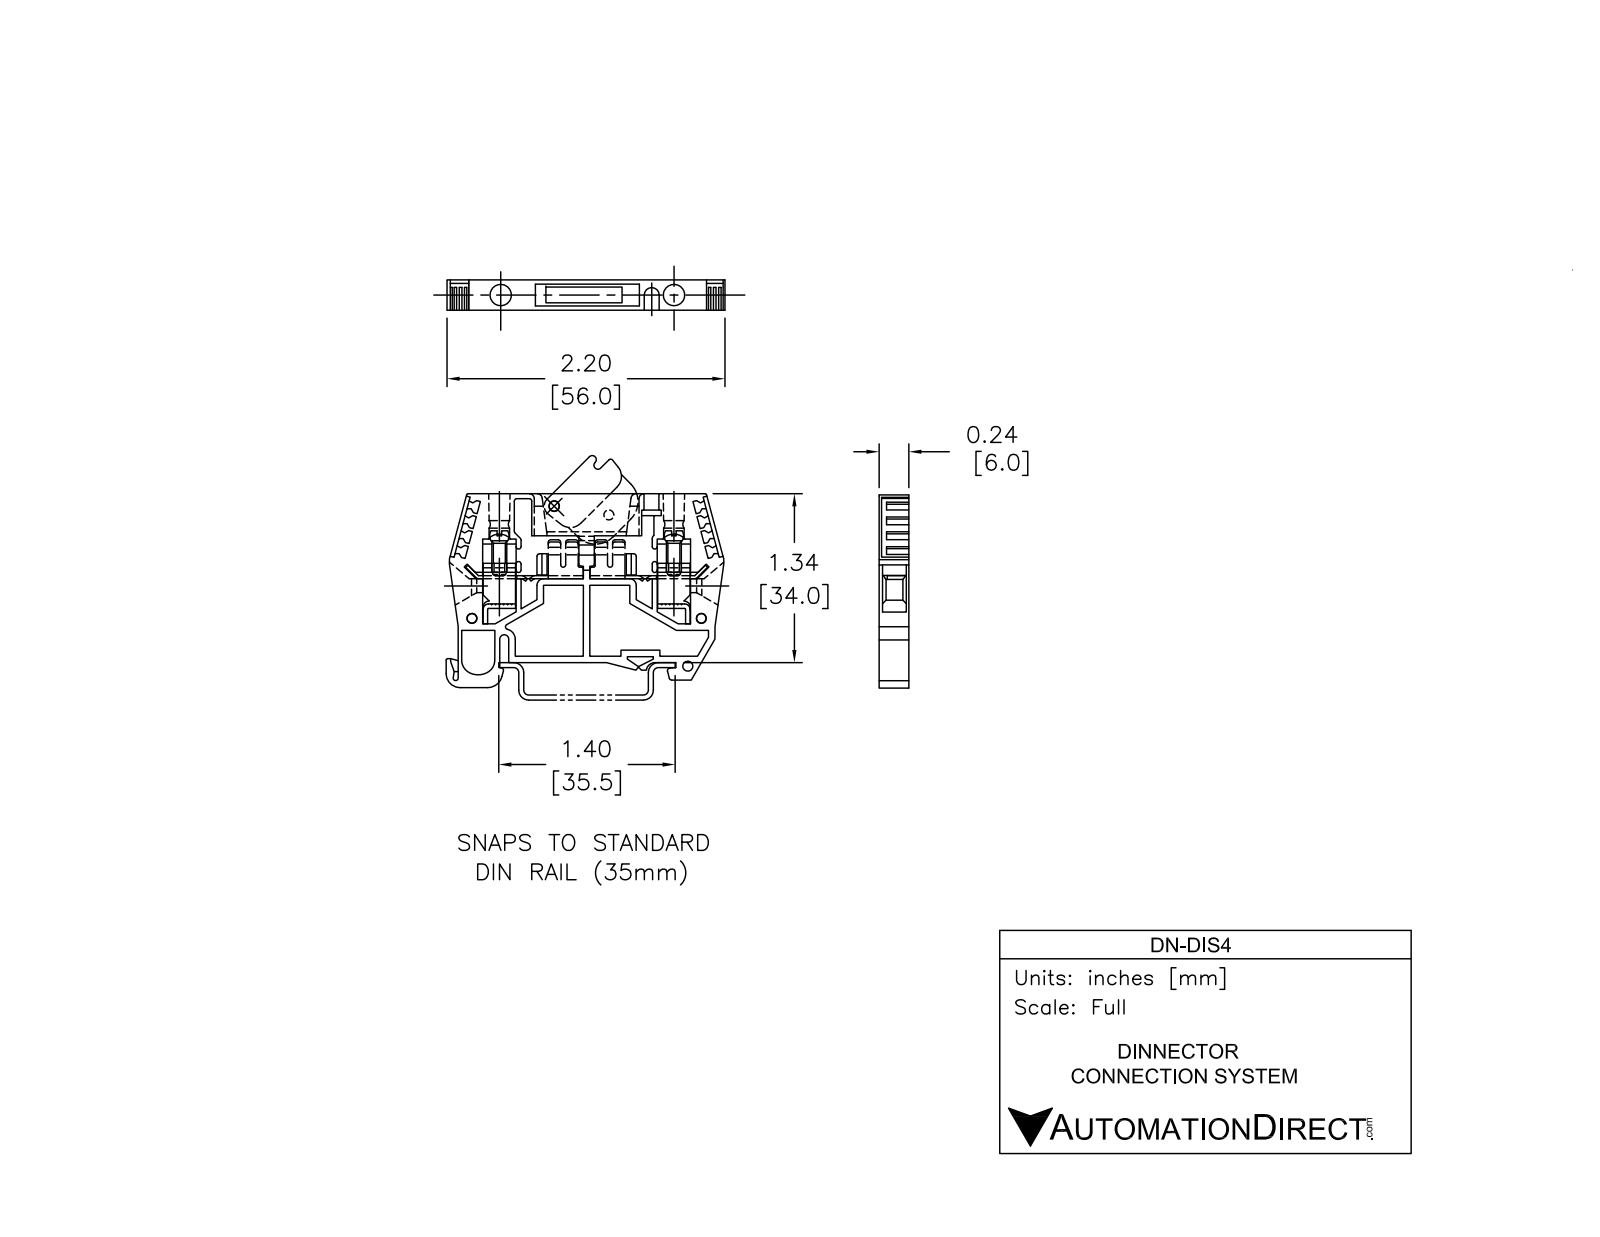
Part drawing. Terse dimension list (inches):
name: 4358103_DN-DIS4; 435K0001; 4258100_DN-QFE4
written by: SolidWorks 2013 (AUTOMOTIVE_DESIGN)
unit: in
bodies: 2 solids, 380 faces (246 planar, 93 cylindrical, 41 other)
size: 2.191 × 1.535 × 0.236
volume: 0.576 in³; area: 11.08 in²
holes: 4× ⌀0.079, 2× ⌀0.161
bosses: 1× ⌀0.079
rounds: 24× R0.02, 7× R0.118, 3× R0.039, 2× R0.031, 2× R0.051, 2× R0.059, 2× R0.197, 1× R0.035
face distances: 0.236, 0.02, 0.138, 0.079, 0.098, 0.108, 0.217, 1.339, 0.024, 0.087
hole spacings: 0.396, 1.041, 1.059, 1.207, 1.378, 1.747, 1.811
